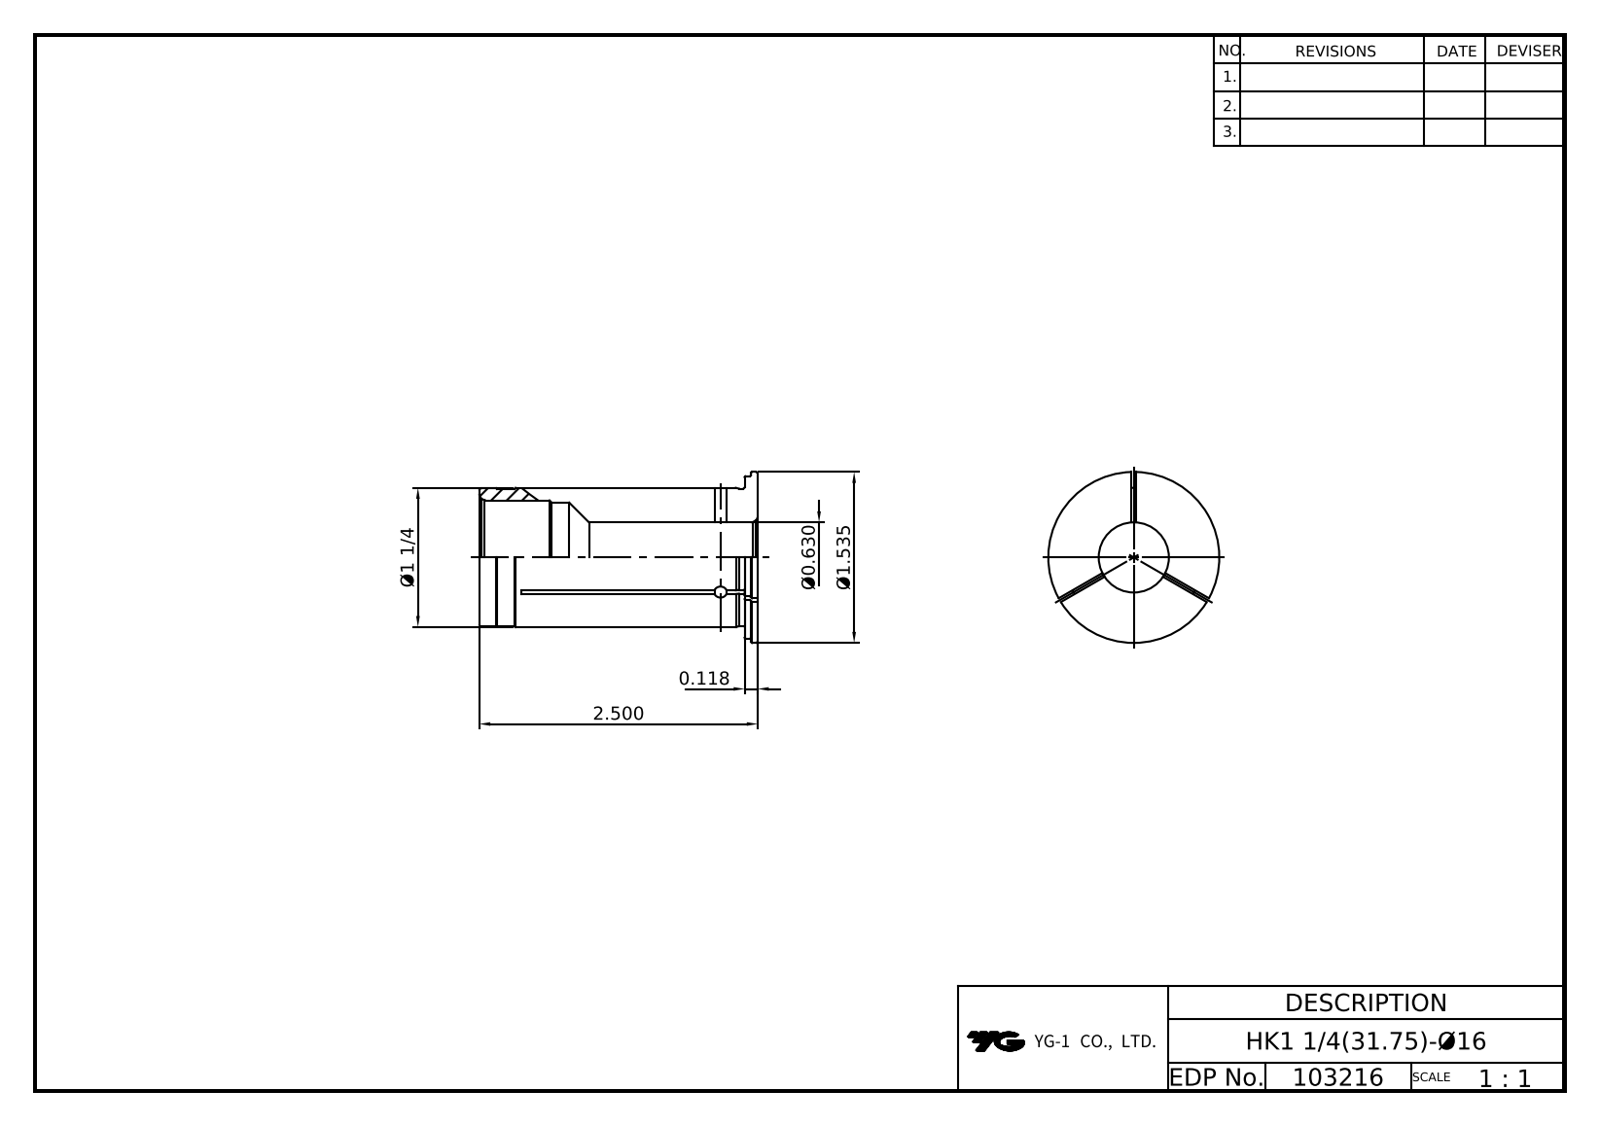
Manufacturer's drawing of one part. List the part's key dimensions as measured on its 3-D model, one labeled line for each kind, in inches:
Part name (STEP PRODUCT): LO-HK31.75-16
STEP written by: Autodesk Inventor 2025 (AP242_MANAGED_MODEL_BASED_3D_ENGINEERING_MIM_LF)
Units: inches
Bodies: 1 solid, 16 faces (4 planar, 6 cylindrical, 6 other)
Overall size (bounding box): 2.5 × 1.535 × 1.535
Volume: 1.912 in³ · Surface area: 18.61 in²
Round holes (diameter × count): ⌀0.63 ×1, ⌀0.984 ×1, ⌀1.024 ×1
Round bosses / shafts (diameter × count): ⌀1.535 ×1, ⌀1.457 ×1, ⌀1.25 ×1
Main face-to-face distances: 2.5, 2.382, 0.118, 0.059, 2.441
